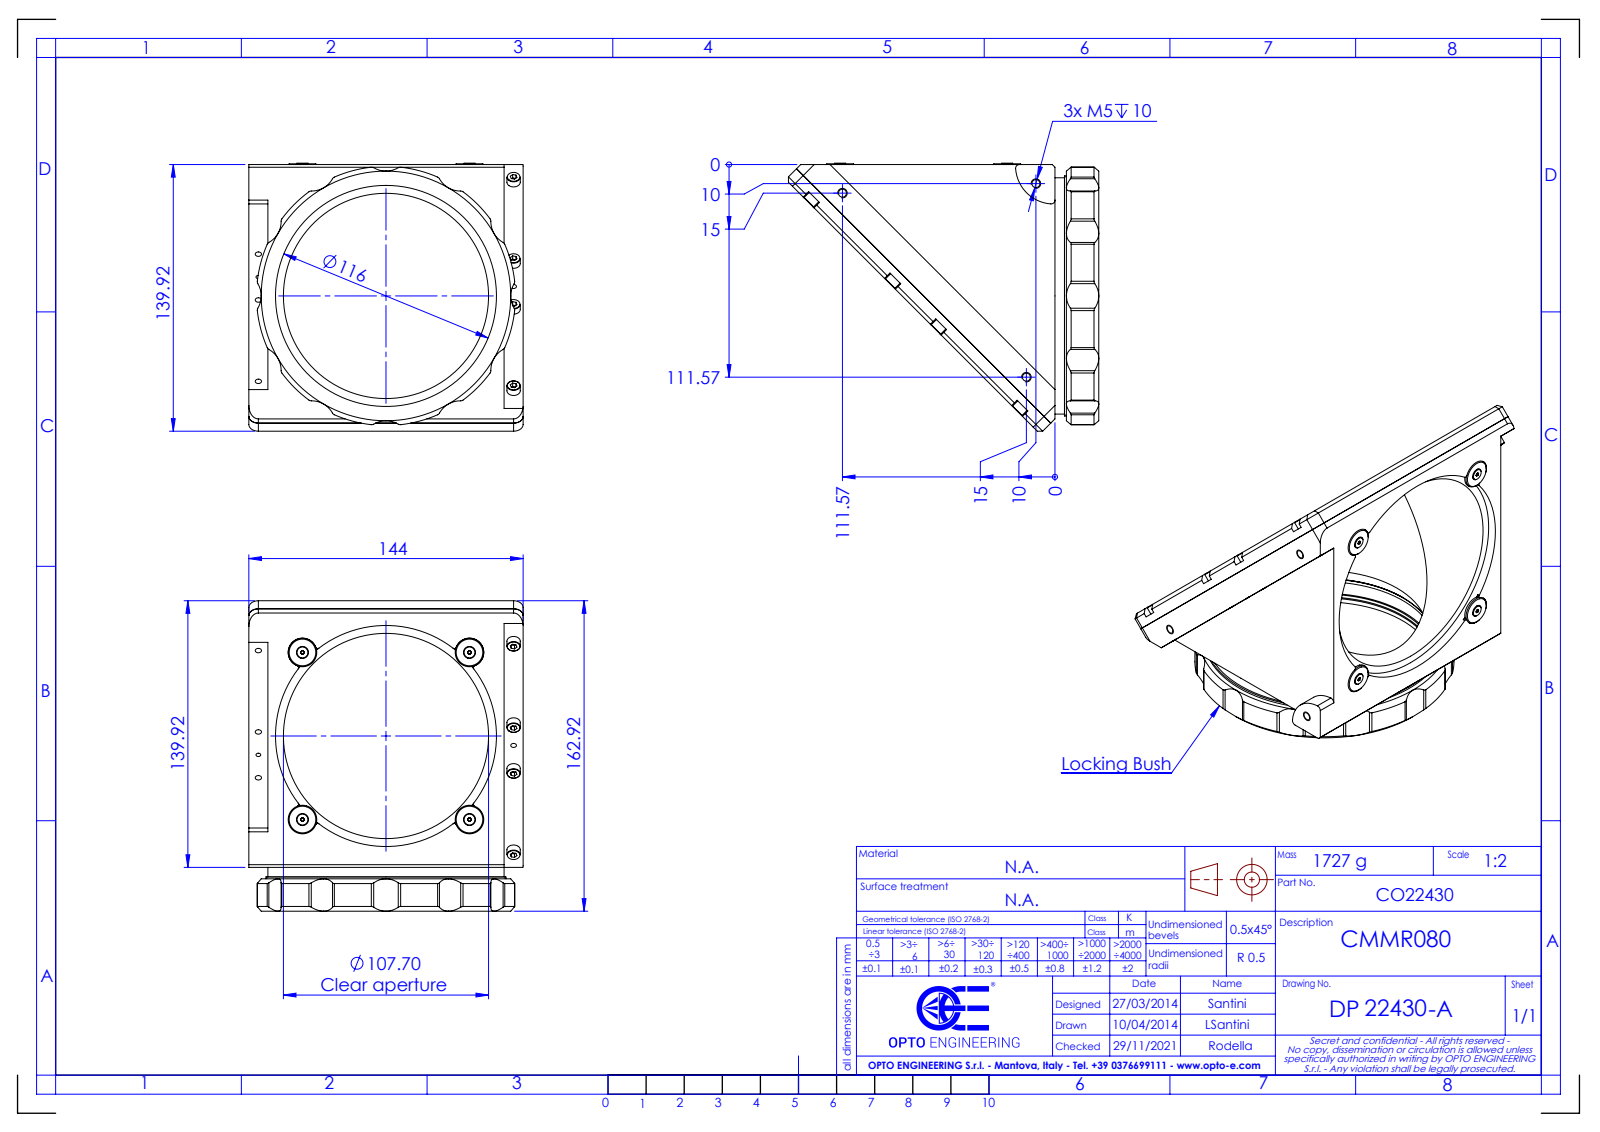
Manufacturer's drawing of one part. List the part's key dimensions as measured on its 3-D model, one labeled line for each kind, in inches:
Part name (STEP PRODUCT): DP22430-A_CMMR080
STEP written by: SolidWorks 2021 (CONFIG_CONTROL_DESIGN)
Units: inches
Bodies: 0 solids, 401 faces (139 planar, 174 cylindrical, 88 other)
Overall size (bounding box): 6.414 × 5.669 × 5.537
Round holes (diameter × count): ⌀0.13 ×8, ⌀0.165 ×3, ⌀0.118 ×2, ⌀4.24 ×2, ⌀4.567 ×2, ⌀0.098 ×1, ⌀4.591 ×1, ⌀4.654 ×1, ⌀4.724 ×1, ⌀4.882 ×1, ⌀4.961 ×1
Round bosses / shafts (diameter × count): ⌀0.276 ×8, ⌀0.591 ×4, ⌀0.226 ×4
Partial cylindrical surfaces — rounded edges, fillets, slot ends (radius × count): R0.079 ×26, R0.492 ×12, R0.039 ×8, R0.157 ×4, R0.197 ×4, R0.787 ×1, R2.677 ×1
Main face-to-face distances: 0.315, 0.394, 4.882, 5.276, 0.276, 0.591, 0.197, 0.906, 5.669, 0.551
Hole centre spacings: 5.276, 0.669, 5.318, 6.453, 6.092, 1.339, 2.377, 2.378
